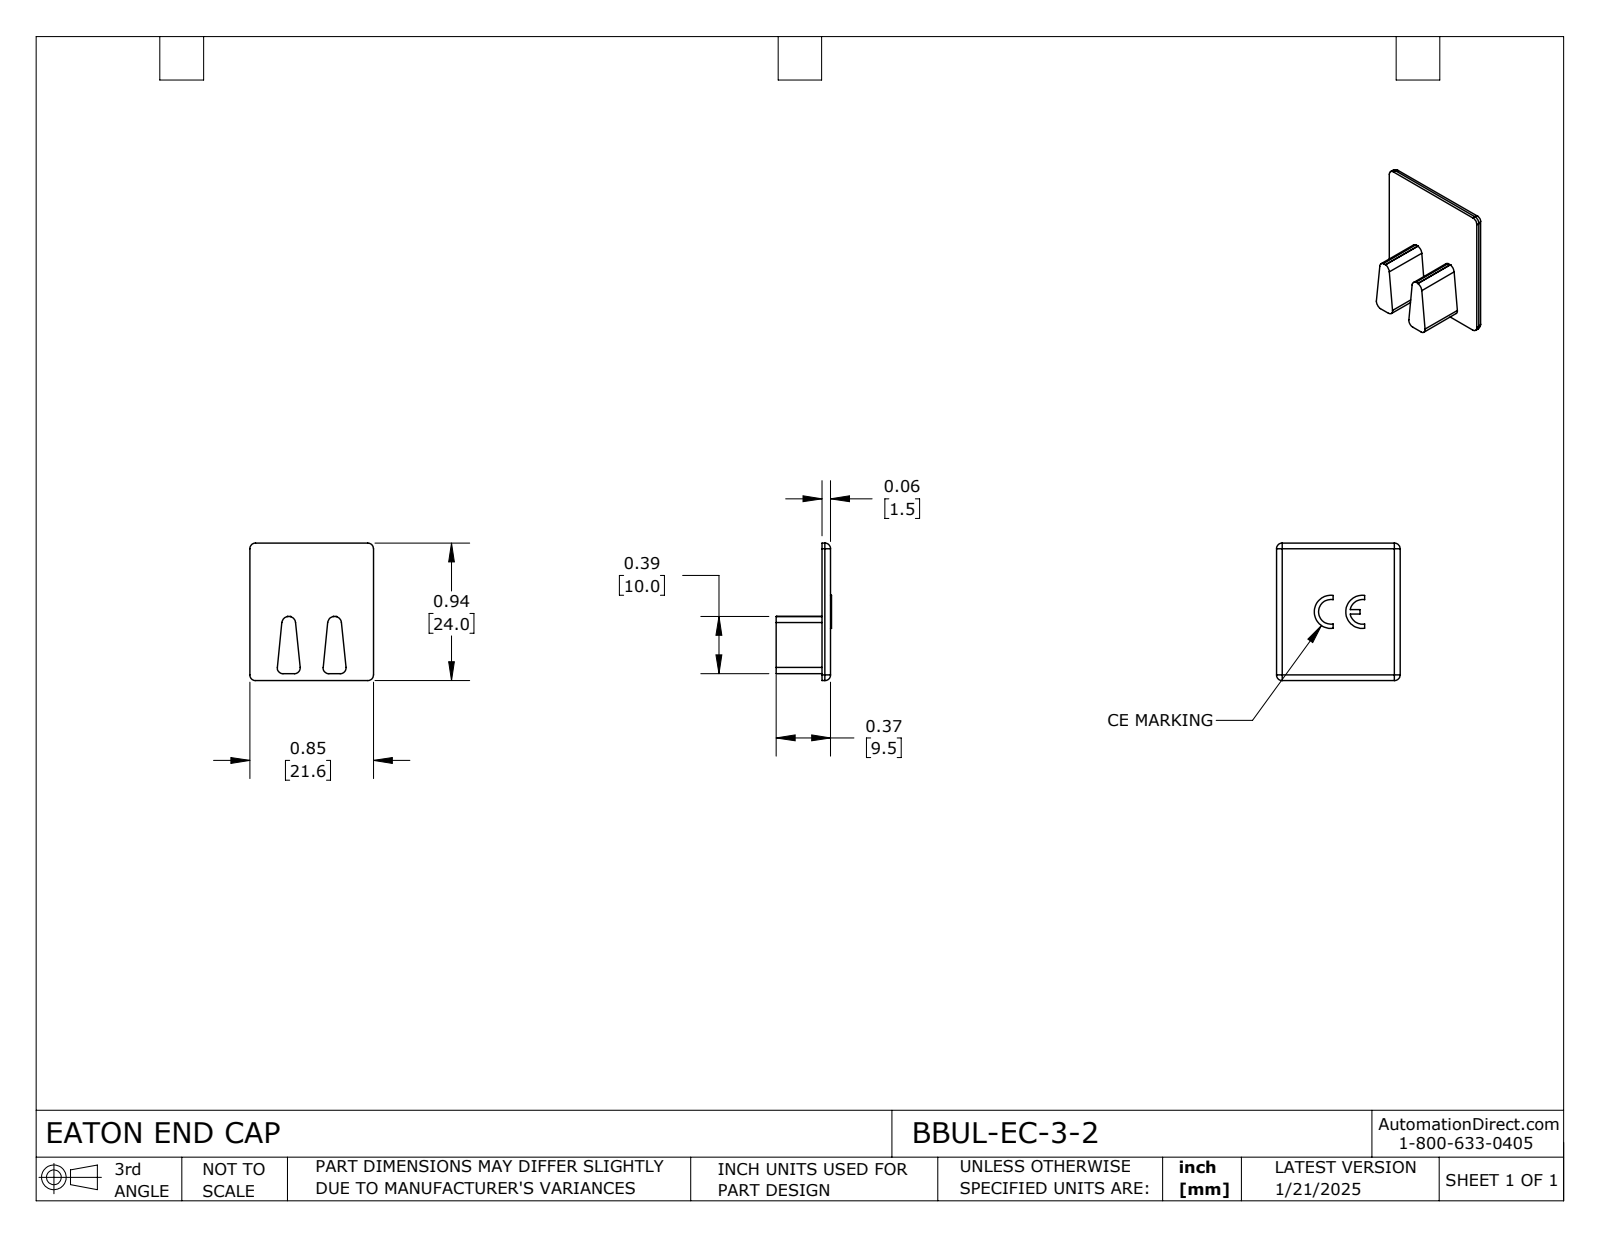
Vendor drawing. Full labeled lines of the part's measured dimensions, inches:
Part name (STEP PRODUCT): BBUL-EC-3-2
STEP written by: SolidWorks 2024 (CONFIG_CONTROL_DESIGN)
Units: inches
Bodies: 1 solid, 56 faces (29 planar, 23 cylindrical, 4 other)
Overall size (bounding box): 0.945 × 0.85 × 0.38
Volume: 0.077 in³ · Surface area: 2.373 in²
Partial cylindrical surfaces — rounded edges, fillets, slot ends (radius × count): R0.039 ×12, R0.047 ×2, R0.085 ×2, R0.114 ×2
Main face-to-face distances: 0.059, 0.313, 0.315, 0.374, 0.065, 0.38, 0.85, 0.047, 0.898, 0.945
